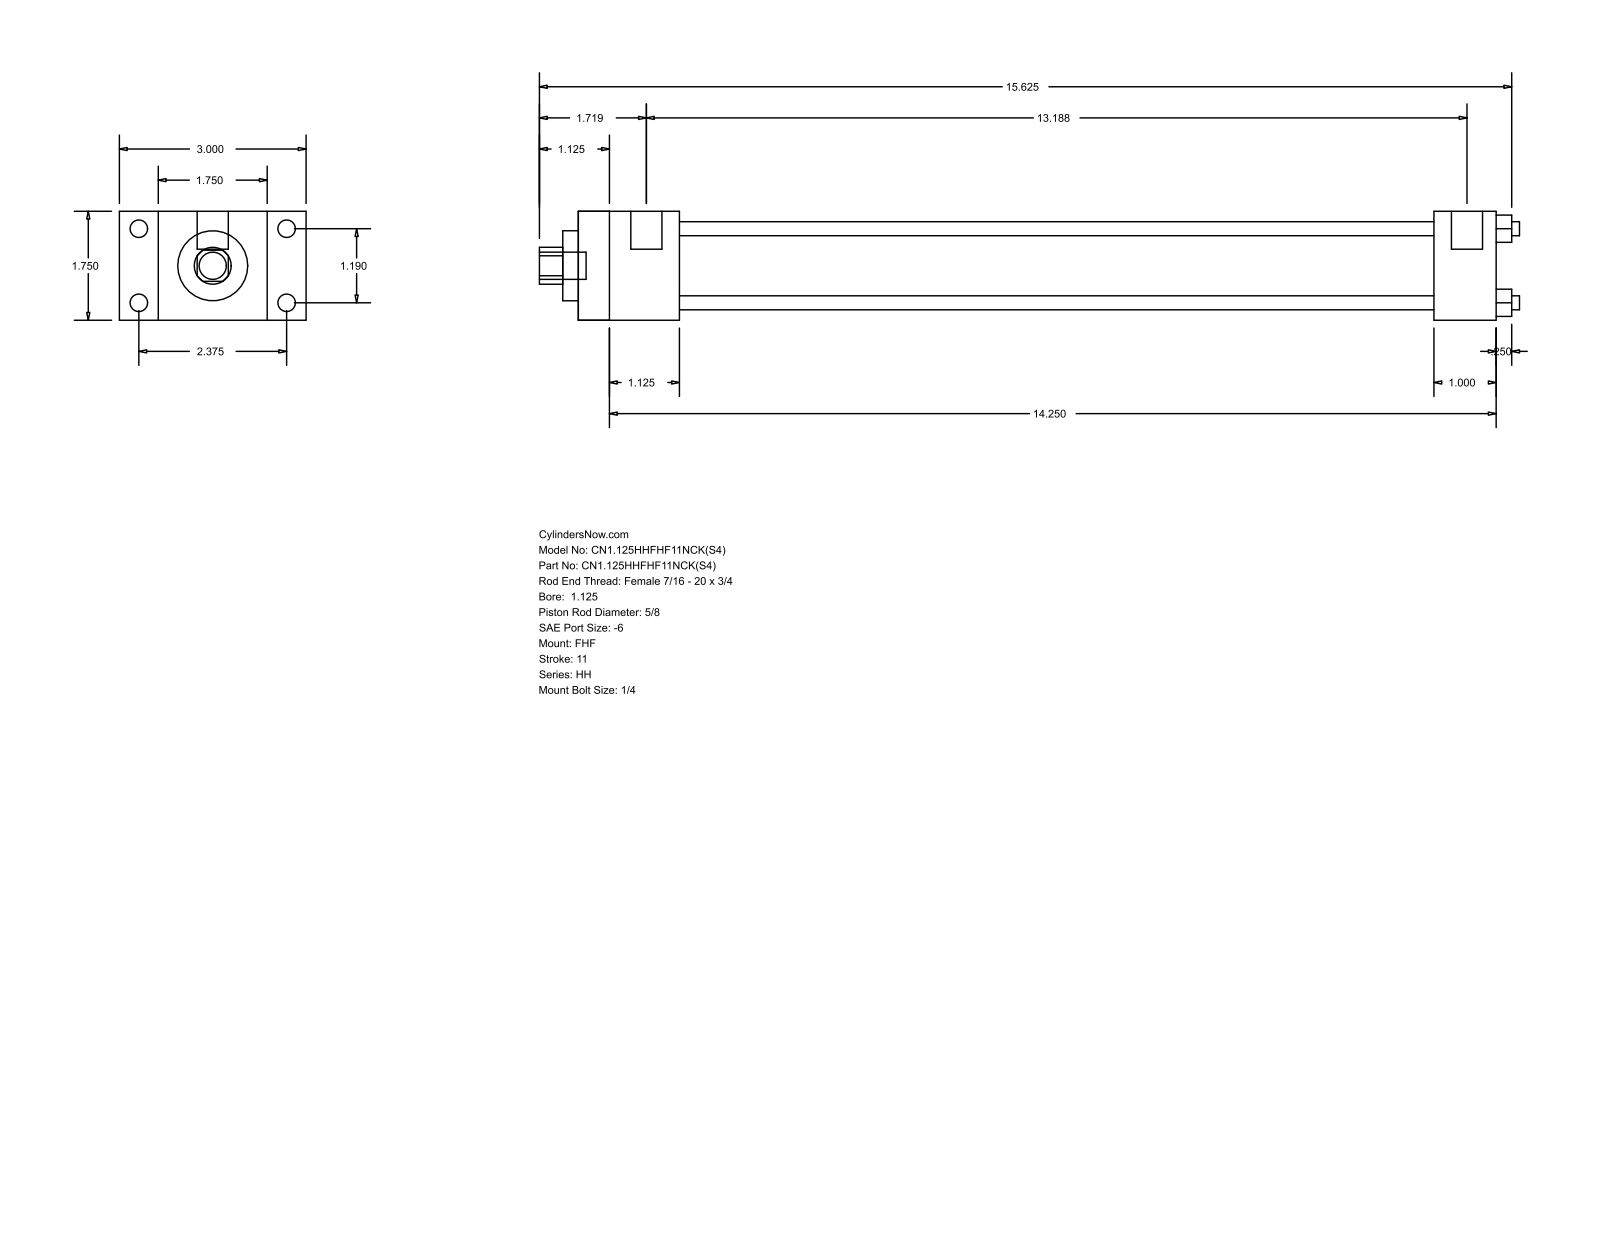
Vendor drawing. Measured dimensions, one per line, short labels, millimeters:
name: HH_FHF__0112_0.625
written by: GSSL Pune (CONFIG_CONTROL_DESIGN)
unit: mm
bodies: 0 solids, 88 faces (60 planar, 28 cylindrical, 0 other)
size: 400.05 × 76.2 × 44.45
holes: 4× ⌀5.71, 1× ⌀15.88, 1× ⌀28.57, 1× ⌀34.92
bosses: 4× ⌀7.14, 4× ⌀5.56, 2× ⌀12.7, 1× ⌀11.11
rounds: 1× R7.54
face distances: 44.46, 15.87, 60.33, 41.27, 76.2, 374.64, 333.37, 349.24, 307.97, 25.4
hole spacings: 21.37, 30.22, 42.74
